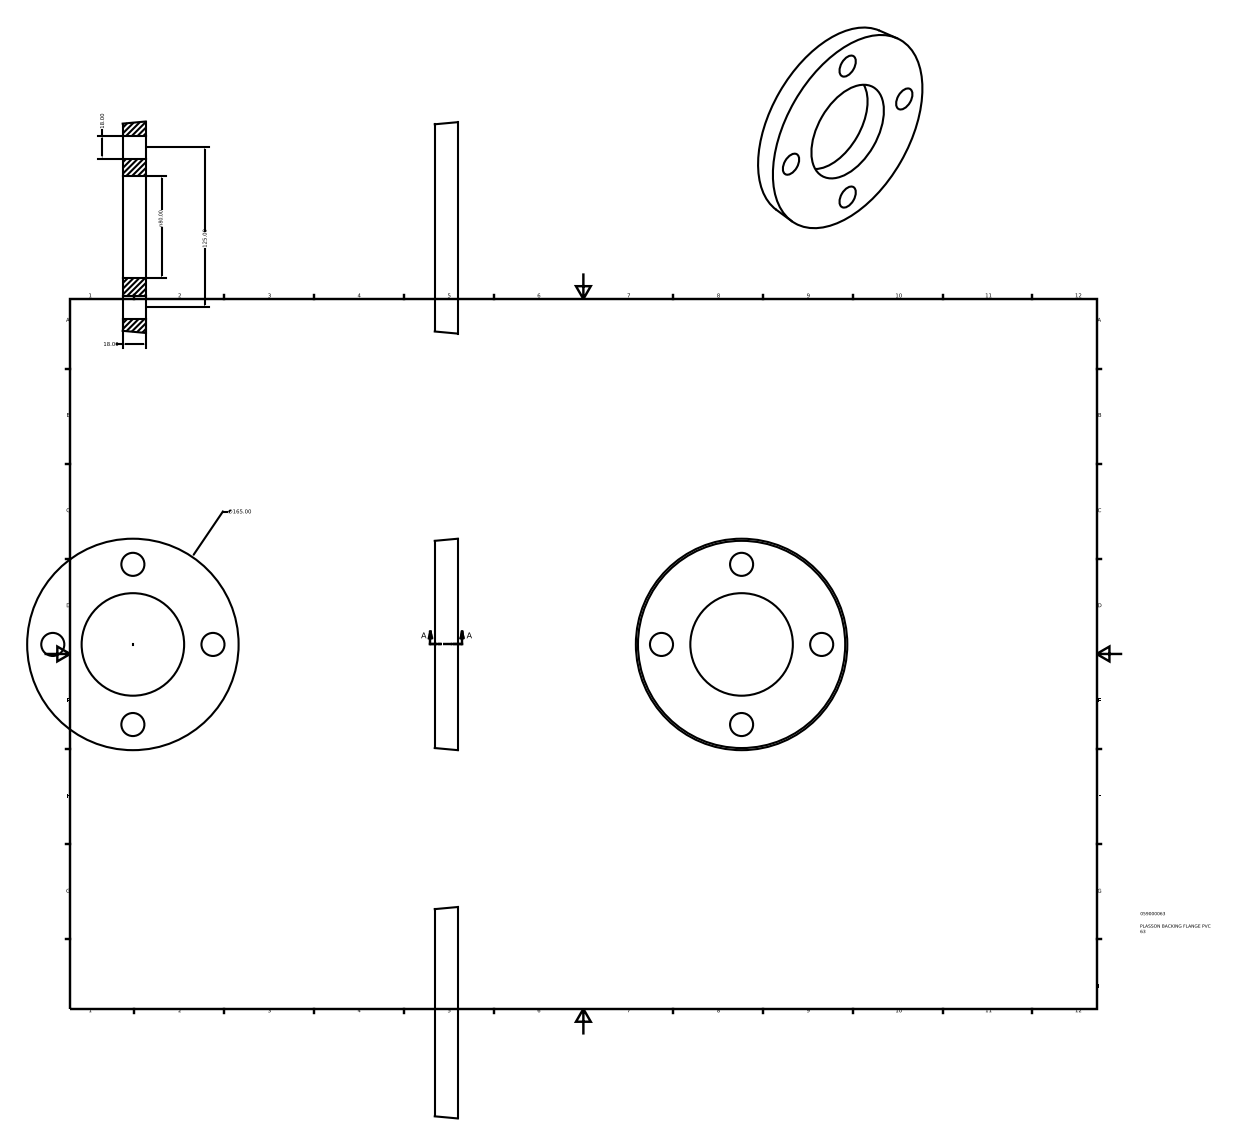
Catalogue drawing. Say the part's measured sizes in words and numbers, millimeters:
The part is named "059000063". Its 3-D file was written by "Autodesk Inventor 2015 (AUTOMOTIVE_DESIGN)". It is 1 solid with 8 faces: 2 planar, 5 cylindrical and 1 other. Overall it measures 165 by 165 by 18 millimeters. Its volume is 268 438 cubic millimeters and its surface area 47 701 square millimeters. Round holes: 4 of diameter 18, 1 of diameter 80. The main face-to-face distances are 18. The hole center spacings are 62.5, 88.39, 125.
